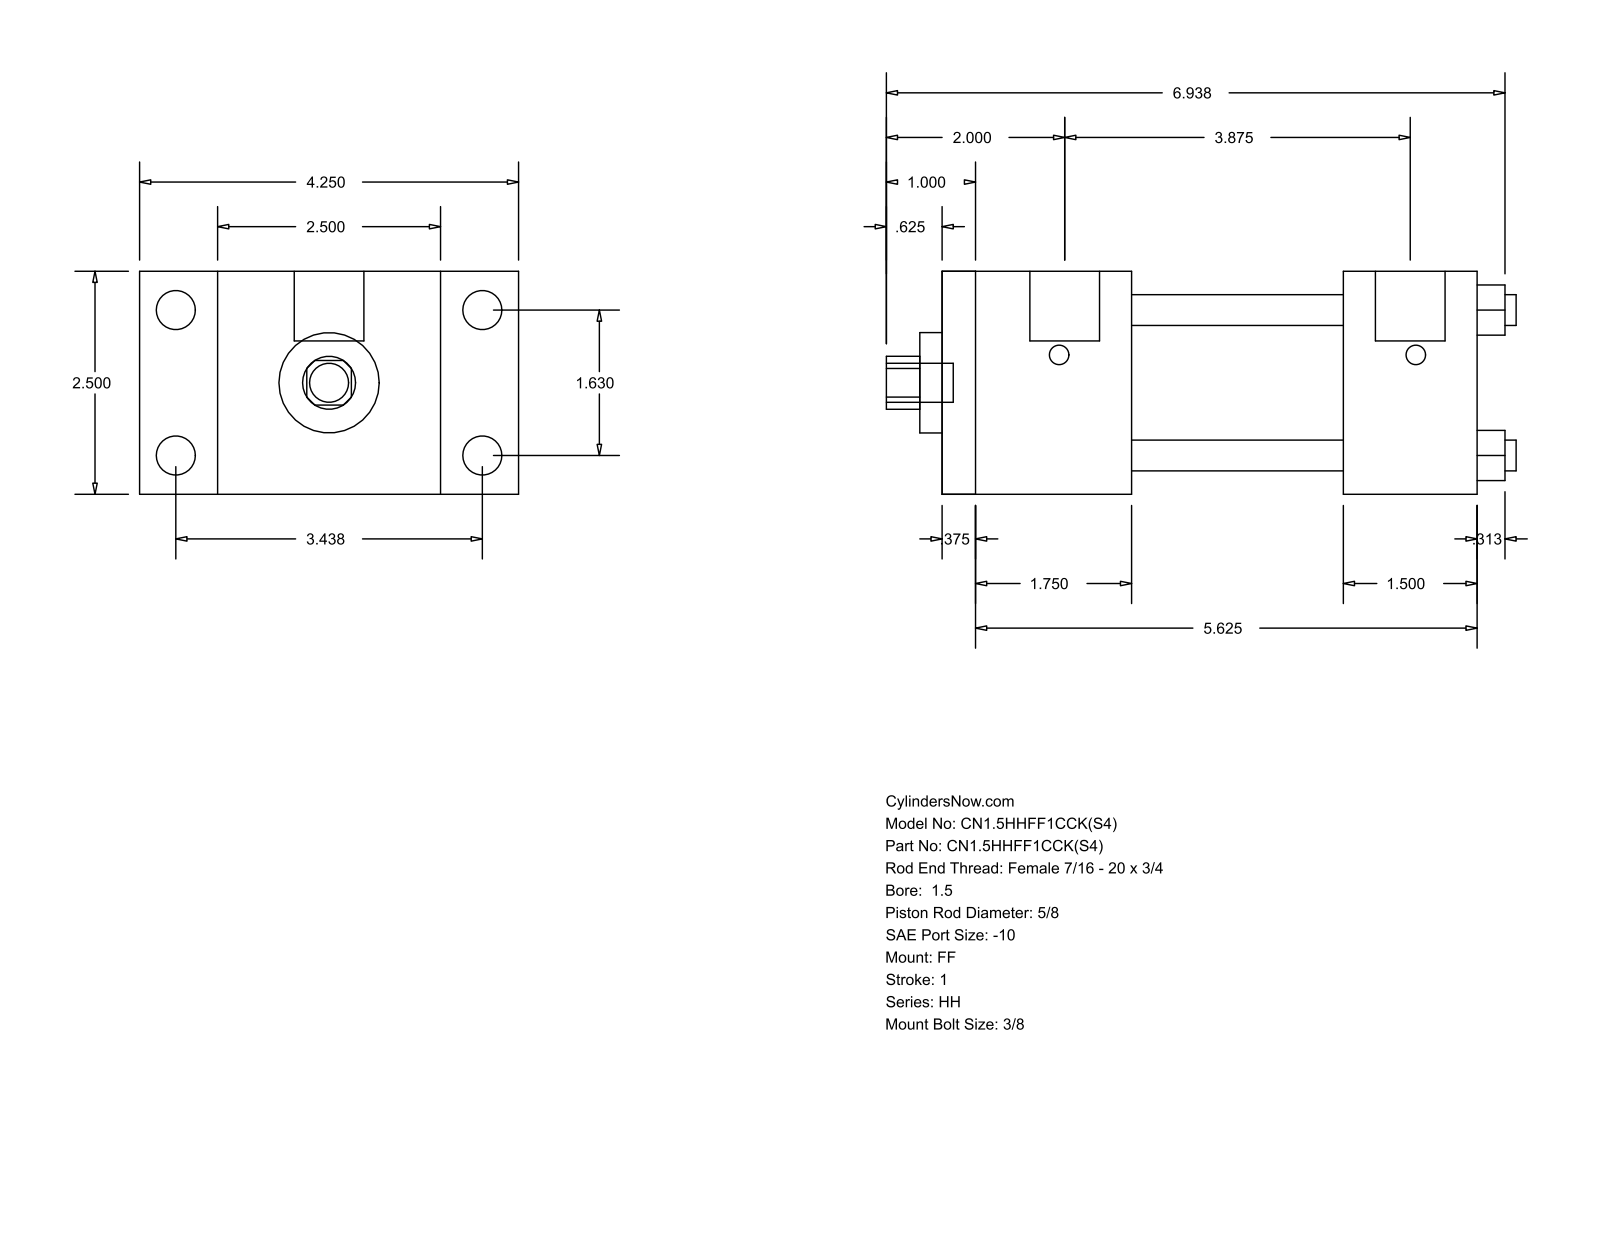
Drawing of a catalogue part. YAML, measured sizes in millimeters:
part_name: "HH_FF__0150_0.625"
step_written_by: "GSSL Pune (CONFIG_CONTROL_DESIGN)"
units: millimeters
bodies: {solids: 0, faces: 92, planar: 64, cylindrical: 28, other: 0}
overall_size: [179.39, 107.95, 63.5]
round_holes:
  - {diameter: 8.76, count: 4}
  - {diameter: 15.88, count: 1}
  - {diameter: 28.57, count: 1}
  - {diameter: 44.45, count: 1}
round_bosses_or_shafts:
  - {diameter: 11.13, count: 4}
  - {diameter: 5.56, count: 4}
  - {diameter: 19.84, count: 2}
  - {diameter: 11.11, count: 1}
partial_cylinders:
  - {radius: 7.54, count: 1}
face_to_face_distances: [63.5, 152.4, 9.52, 38.1, 142.88, 60.33, 53.97, 44.45, 98.43, 114.3]
hole_center_spacings: [29.27, 41.4, 58.55]
